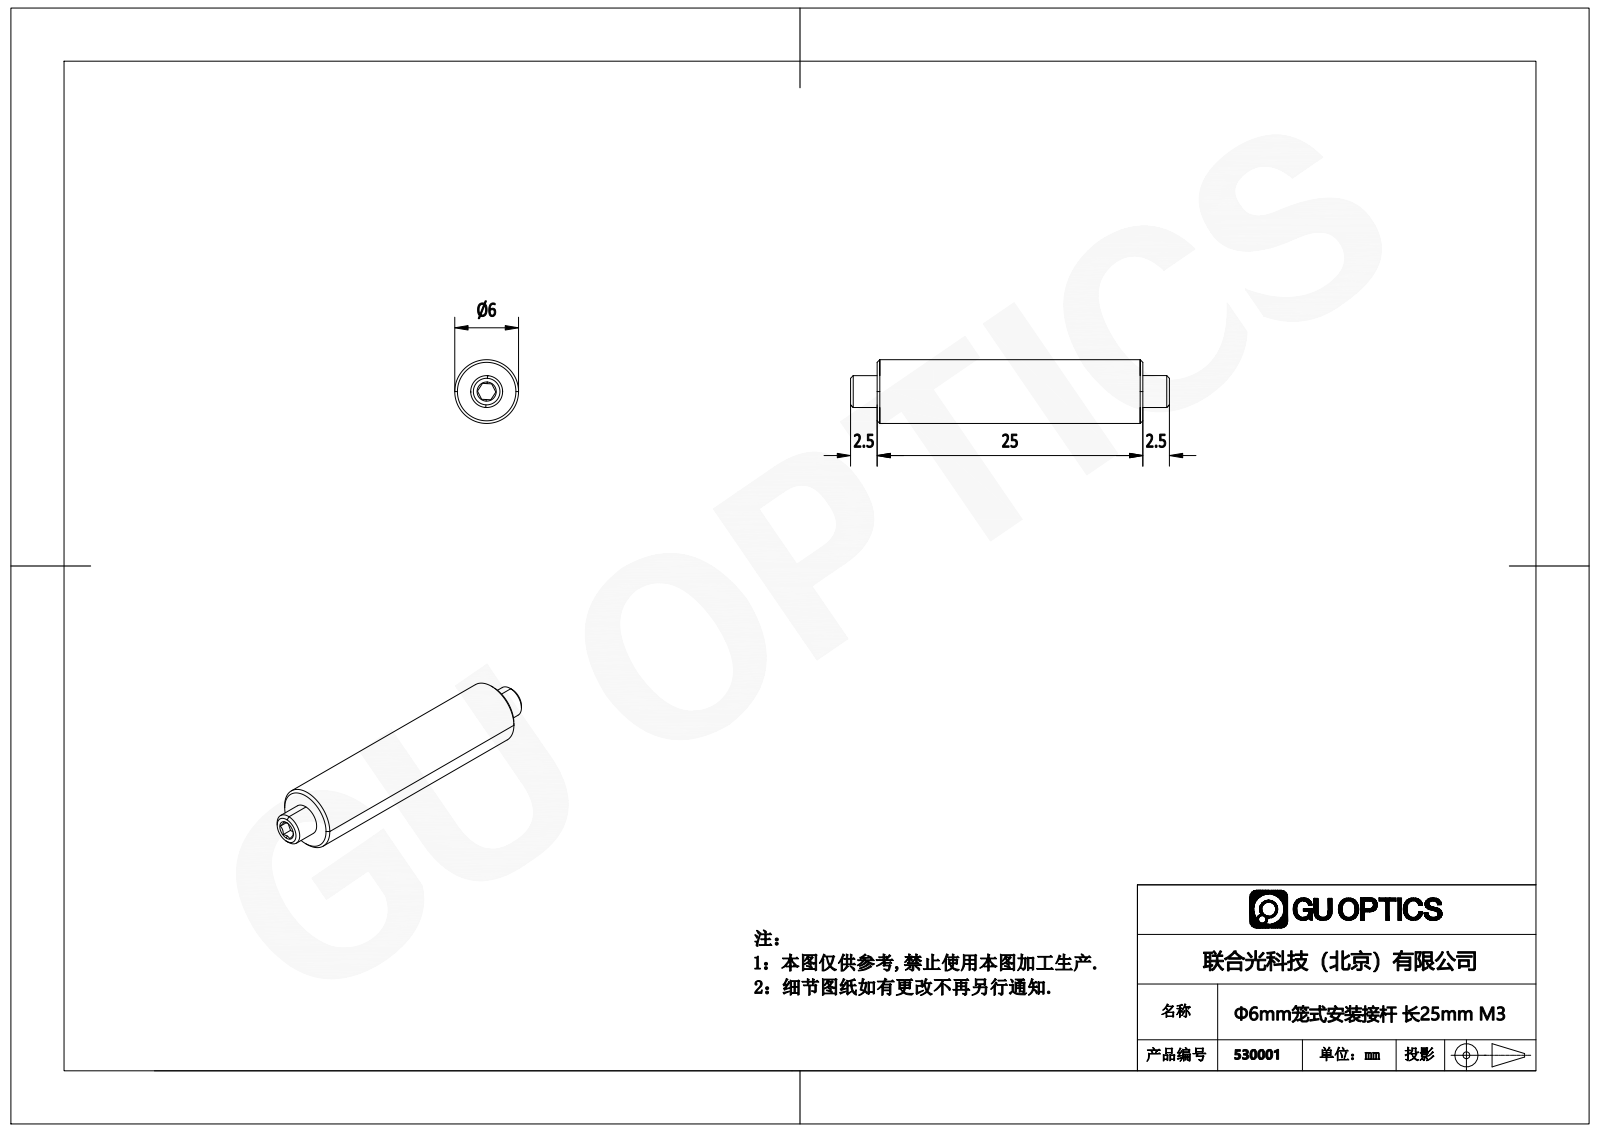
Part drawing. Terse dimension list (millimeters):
written by: SolidWorks 2018 (AUTOMOTIVE_DESIGN)
unit: mm
bodies: 0 solids, 36 faces (18 planar, 6 cylindrical, 12 other)
size: 30 × 6 × 6
bosses: 1× ⌀6, 1× ⌀3
face distances: 25, 1.5, 2.5, 27.5, 1, 29, 26.5, 30, 28
